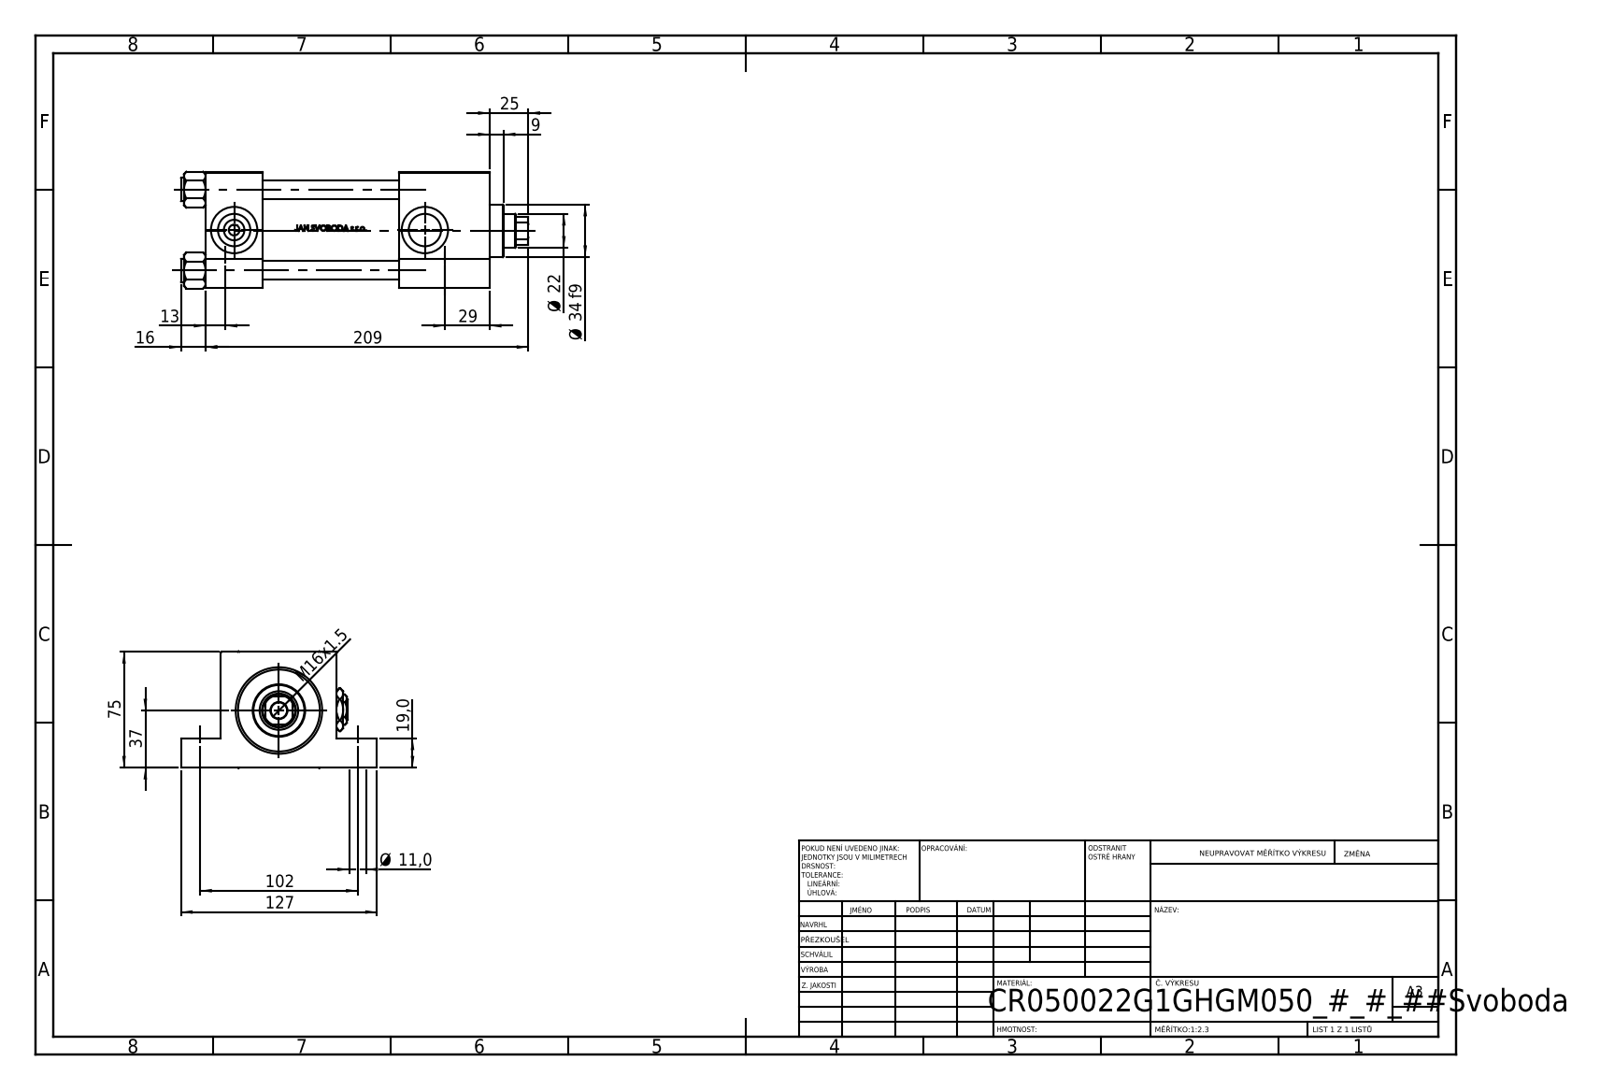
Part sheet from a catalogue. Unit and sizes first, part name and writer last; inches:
Units: inches
Overall size (bounding box): 8.858 × 5 × 2.974
Round holes (diameter × count): ⌀0.433 ×4, ⌀0.472 ×4, ⌀0.276 ×2, ⌀0.825 ×2, ⌀1.181 ×2, ⌀0.413 ×1, ⌀0.866 ×1, ⌀0.984 ×1, ⌀1.614 ×1, ⌀1.969 ×1, ⌀2.087 ×1
Round bosses / shafts (diameter × count): ⌀0.591 ×4, ⌀2.205 ×1, ⌀1.339 ×1
Partial cylindrical surfaces — rounded edges, fillets, slot ends (radius × count): R0.413 ×1
Main face-to-face distances: 2.953, 1.457, 7.244, 5.787, 0.748, 2.205, 3.976, 4.921, 3.465, 2.323
Hole centre spacings: 2.059, 1.442, 1.47, 2.912, 4.016, 5.591, 6.883, 4.862
Volume: 48.35 in³ · Surface area: 275.7 in²
Bodies: 12 solids, 1134 faces (454 planar, 128 cylindrical, 552 other)
Part name (STEP PRODUCT): V215CR_G_TYCINKA; NUT_M5_G; V215CR_VCP_G; V215CR_G_Body (+2 more)
STEP written by: SolidWorks 2019 (CONFIG_CONTROL_DESIGN)
